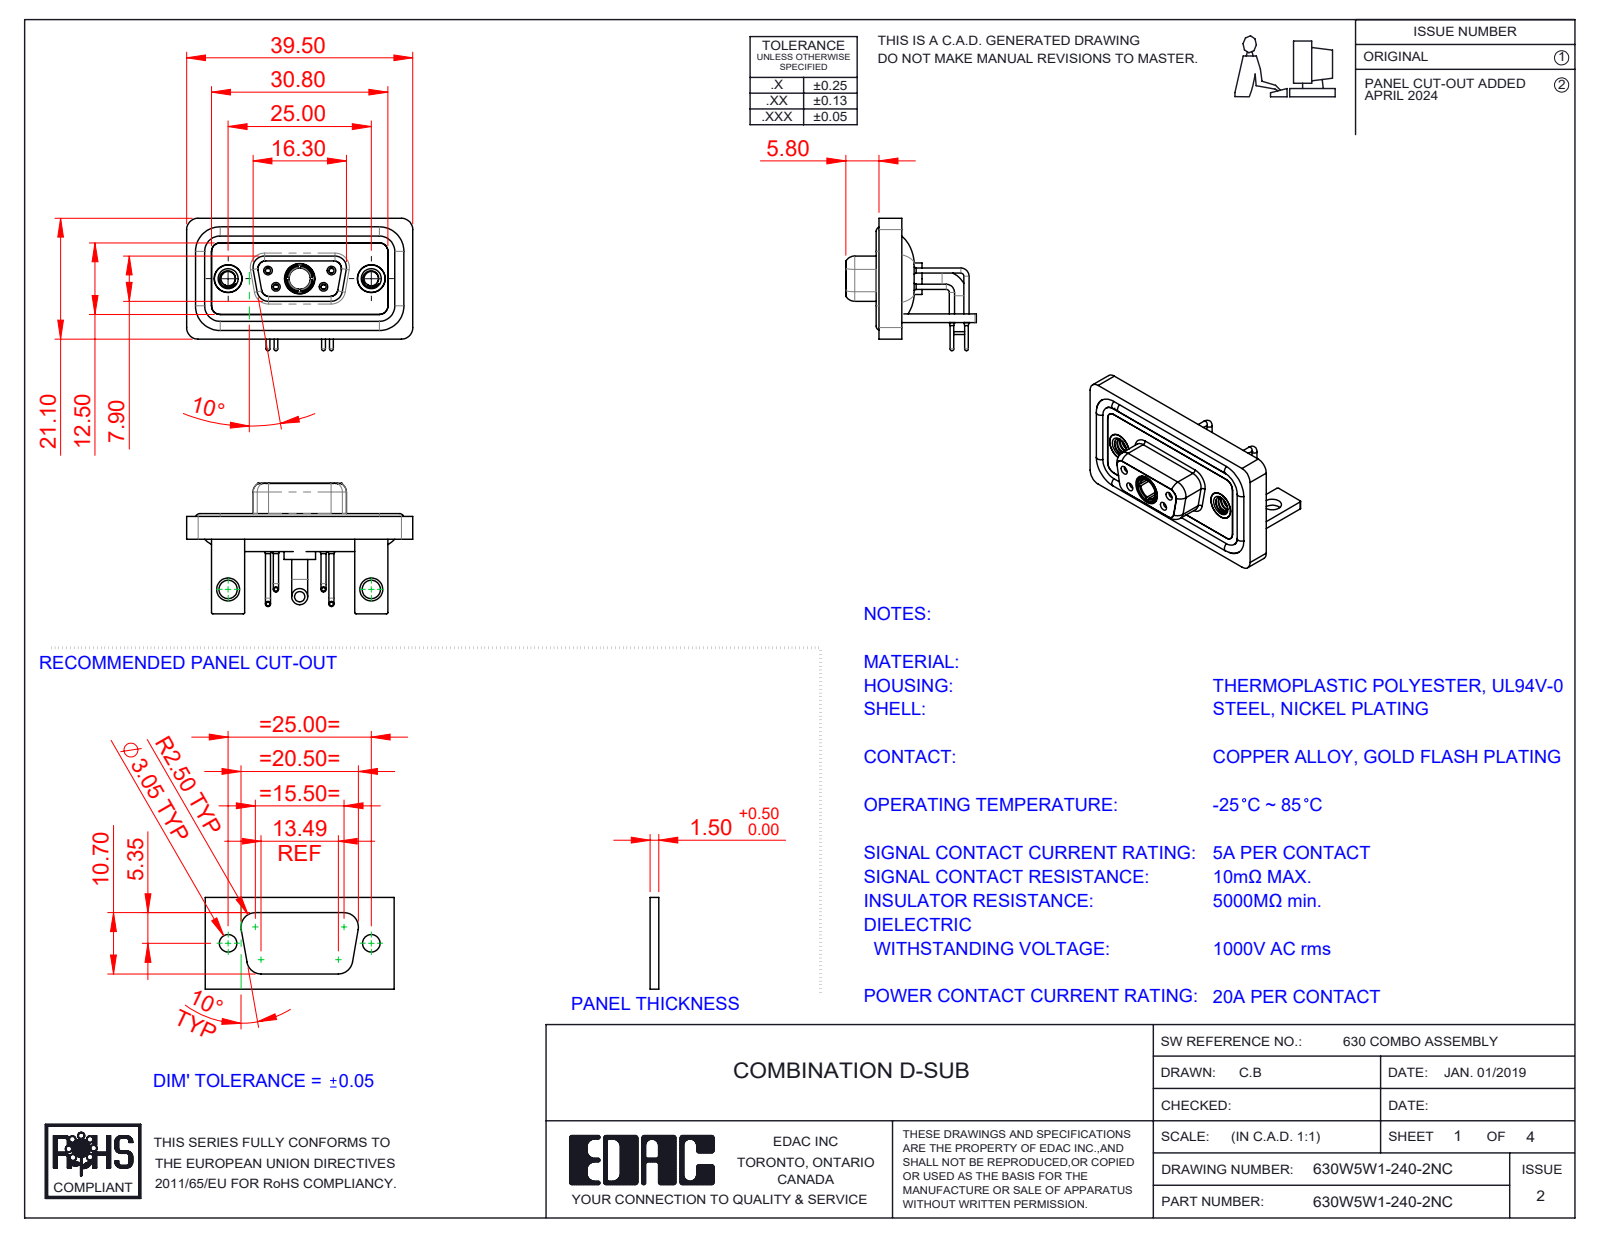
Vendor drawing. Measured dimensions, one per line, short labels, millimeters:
name: Power Socket_20A RA; 630Combo Waterproof Housing_09 Contacts; 630Combo Shell Front_09 Contacts; 630Combo Shell Rear_09 Contacts (+6 more)
written by: SolidWorks 2023 (CONFIG_CONTROL_DESIGN)
unit: mm
bodies: 15 solids, 718 faces (214 planar, 327 cylindrical, 177 other)
size: 39.5 × 23.12 × 22.8
volume: 5 188 mm³; area: 8 582 mm²
holes: 4× ⌀0.9, 4× ⌀1.1, 4× ⌀1.5, 4× ⌀2, 3× ⌀4.85, 2× ⌀1.6, 2× ⌀1.7, 2× ⌀2.5, 2× ⌀3.2, 2× ⌀4, 2× ⌀4.05, 2× ⌀5
bosses: 6× ⌀1.6, 4× ⌀0.9, 4× ⌀0.65, 2× ⌀4.95, 2× ⌀4.8, 2× ⌀2.8, 1× ⌀5.5, 1× ⌀5.2
rounds: 19× R2, 18× R1.5, 16× R0.25, 8× R1.35, 8× R1.6, 5× R0.5, 4× R0.6, 4× R0.65
face distances: 0.4, 2.9, 1.5, 1.8, 1.1, 3.7, 1.6, 0.8, 2.5, 3.1
hole spacings: 3.16, 5.72, 7.1, 12.5, 18.1, 25, 4.39, 4.4
